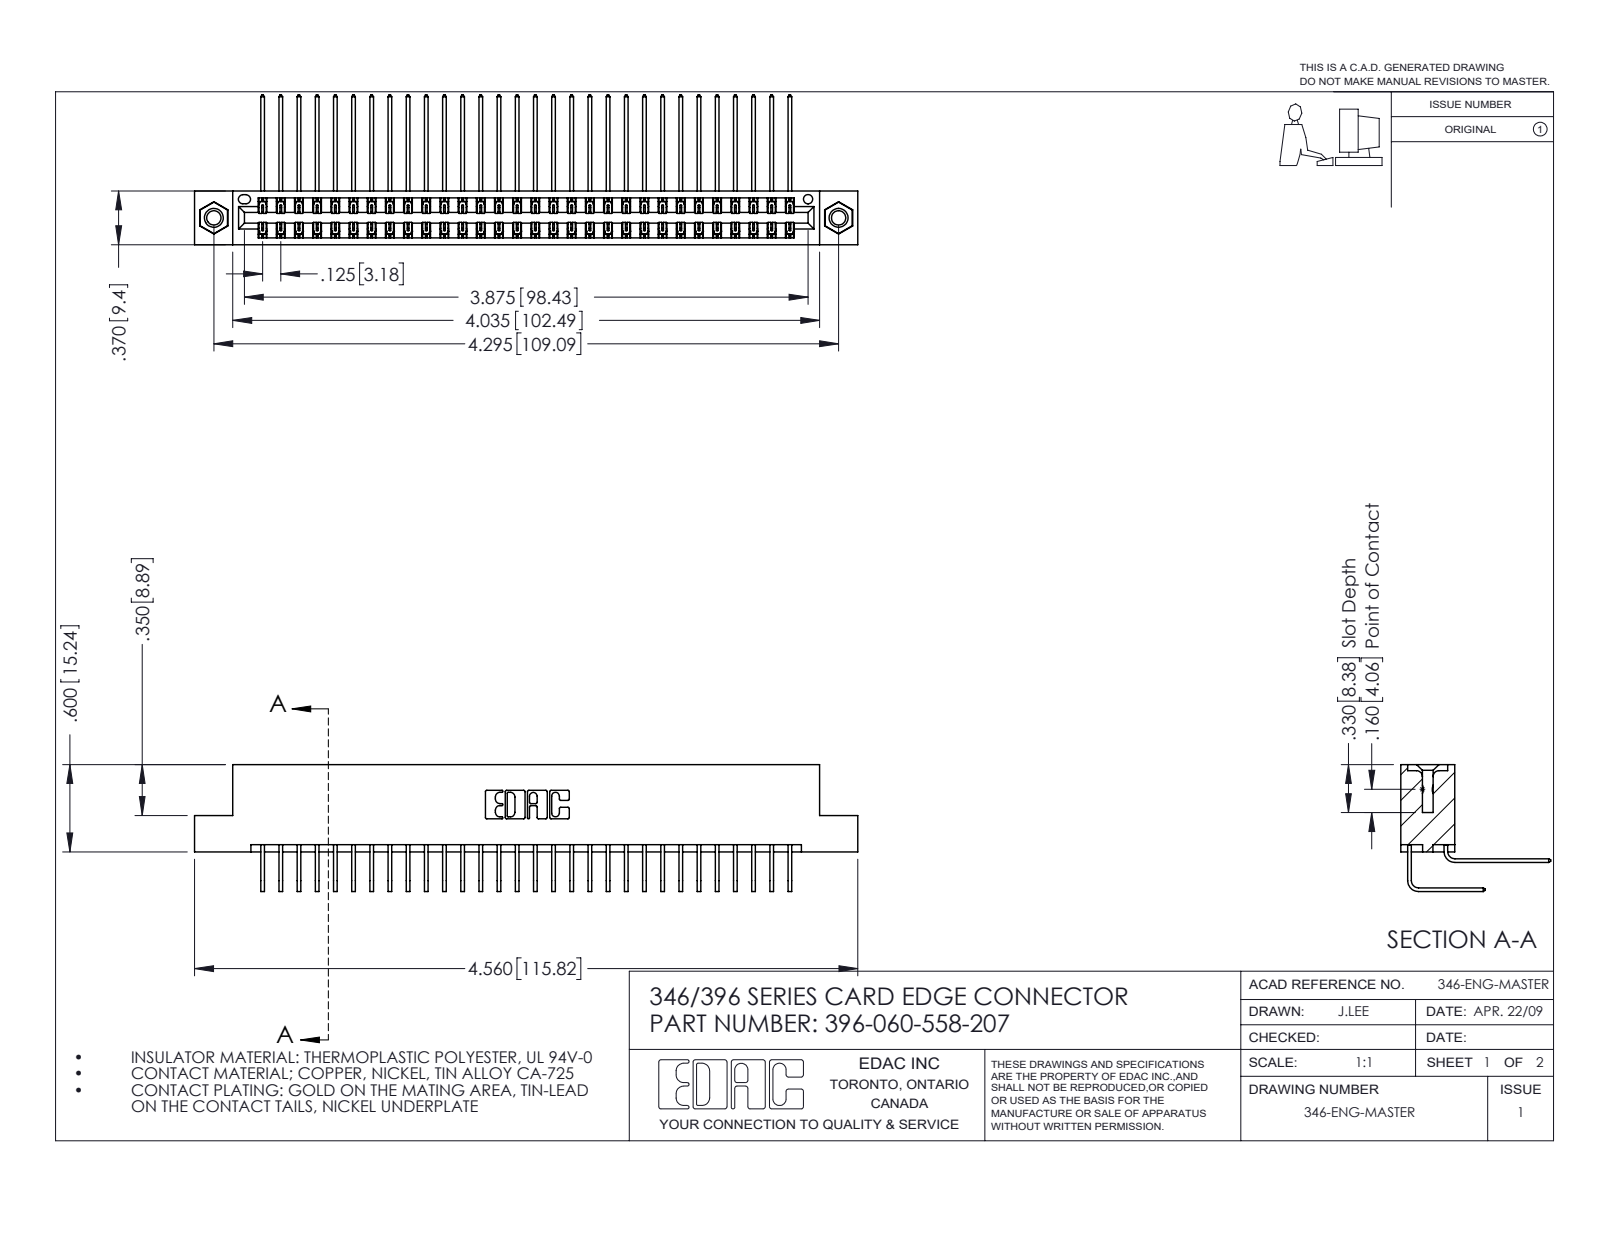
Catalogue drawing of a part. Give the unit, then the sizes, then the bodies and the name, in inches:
Units: inches
Overall size (bounding box): 4.56 × 1.03 × 0.873
Round holes (diameter × count): ⌀0.098 ×2, ⌀0.125 ×2, ⌀0.156 ×2, ⌀0.064 ×1
Round bosses / shafts (diameter × count): ⌀0.155 ×2
Partial cylindrical surfaces — rounded edges, fillets, slot ends (radius × count): R0.006 ×90, R0.01 ×22, R0.007 ×6, R0.031 ×6, R0.026 ×3, R0.014 ×2, R0.022 ×2, R0.024 ×2
Main face-to-face distances: 0.048, 0.322, 0.025, 0.25, 0.37, 0.072, 0.298, 0.275, 0.148, 0.222
Hole centre spacings: 0.246, 4.087, 4.295
Volume: 0.704 in³ · Surface area: 26.91 in²
Bodies: 63 solids, 3422 faces (2328 planar, 1078 cylindrical, 16 other)
Part name (STEP PRODUCT): 345-250-001_345-250-005-103; 345-292-001_558 Tail - 2; 345-292-001_558 559 Tail - 1; 346 Part_Flush Mounting Lugs - 0.156 Dia-TI (+1 more)
STEP written by: SolidWorks 2016 (CONFIG_CONTROL_DESIGN)
